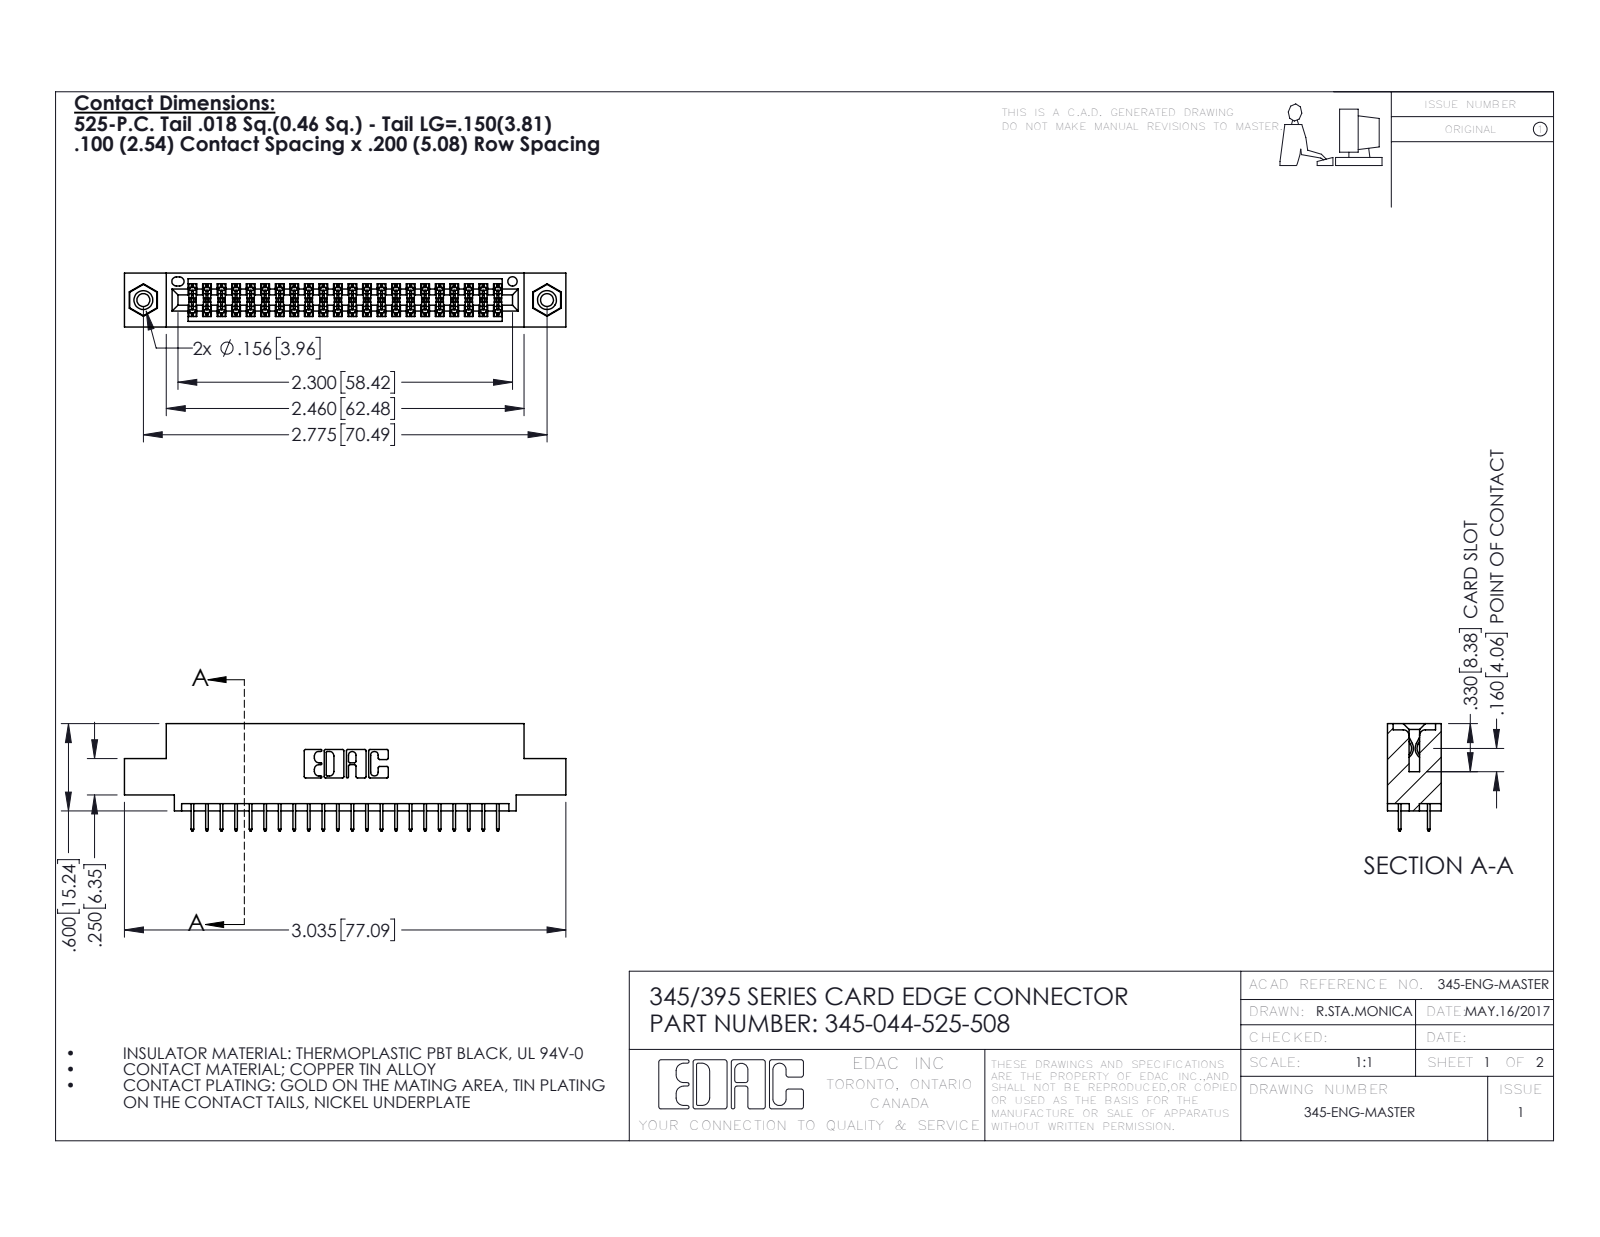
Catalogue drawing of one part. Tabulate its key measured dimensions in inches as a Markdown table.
| quantity | value |
| --- | --- |
| part name | 345-250-001_345-250-003-102; 345-292-001_345-293-125; 345-044-525-508; 345 Part_0.110 Offset - 0.156 Dia-TI |
| STEP written by | SolidWorks 2020 (CONFIG_CONTROL_DESIGN) |
| units | inches |
| bodies | 47 solids, 2566 faces (1832 planar, 718 cylindrical, 16 other) |
| overall size | 3.035 × 0.737 × 0.37 |
| volume | 0.436 in³ |
| surface area | 15.61 in² |
| round holes (diameter × count) | 0.089 × 2, 0.125 × 2, 0.156 × 2, 0.064 × 1 |
| round bosses / shafts (diameter × count) | 0.155 × 2 |
| partial cylindrical surfaces (radius × count) | 0.006 × 66, 0.01 × 22, 0.007 × 6, 0.031 × 6, 0.026 × 3, 0.014 × 2, 0.019 × 2, 0.022 × 2 |
| main face-to-face distances | 0.072, 0.298, 0.2, 0.37, 0.098, 0.272, 0.025, 0.225, 0.072, 0.175 |
| hole center spacings | 0.27, 2.541, 2.775 |
